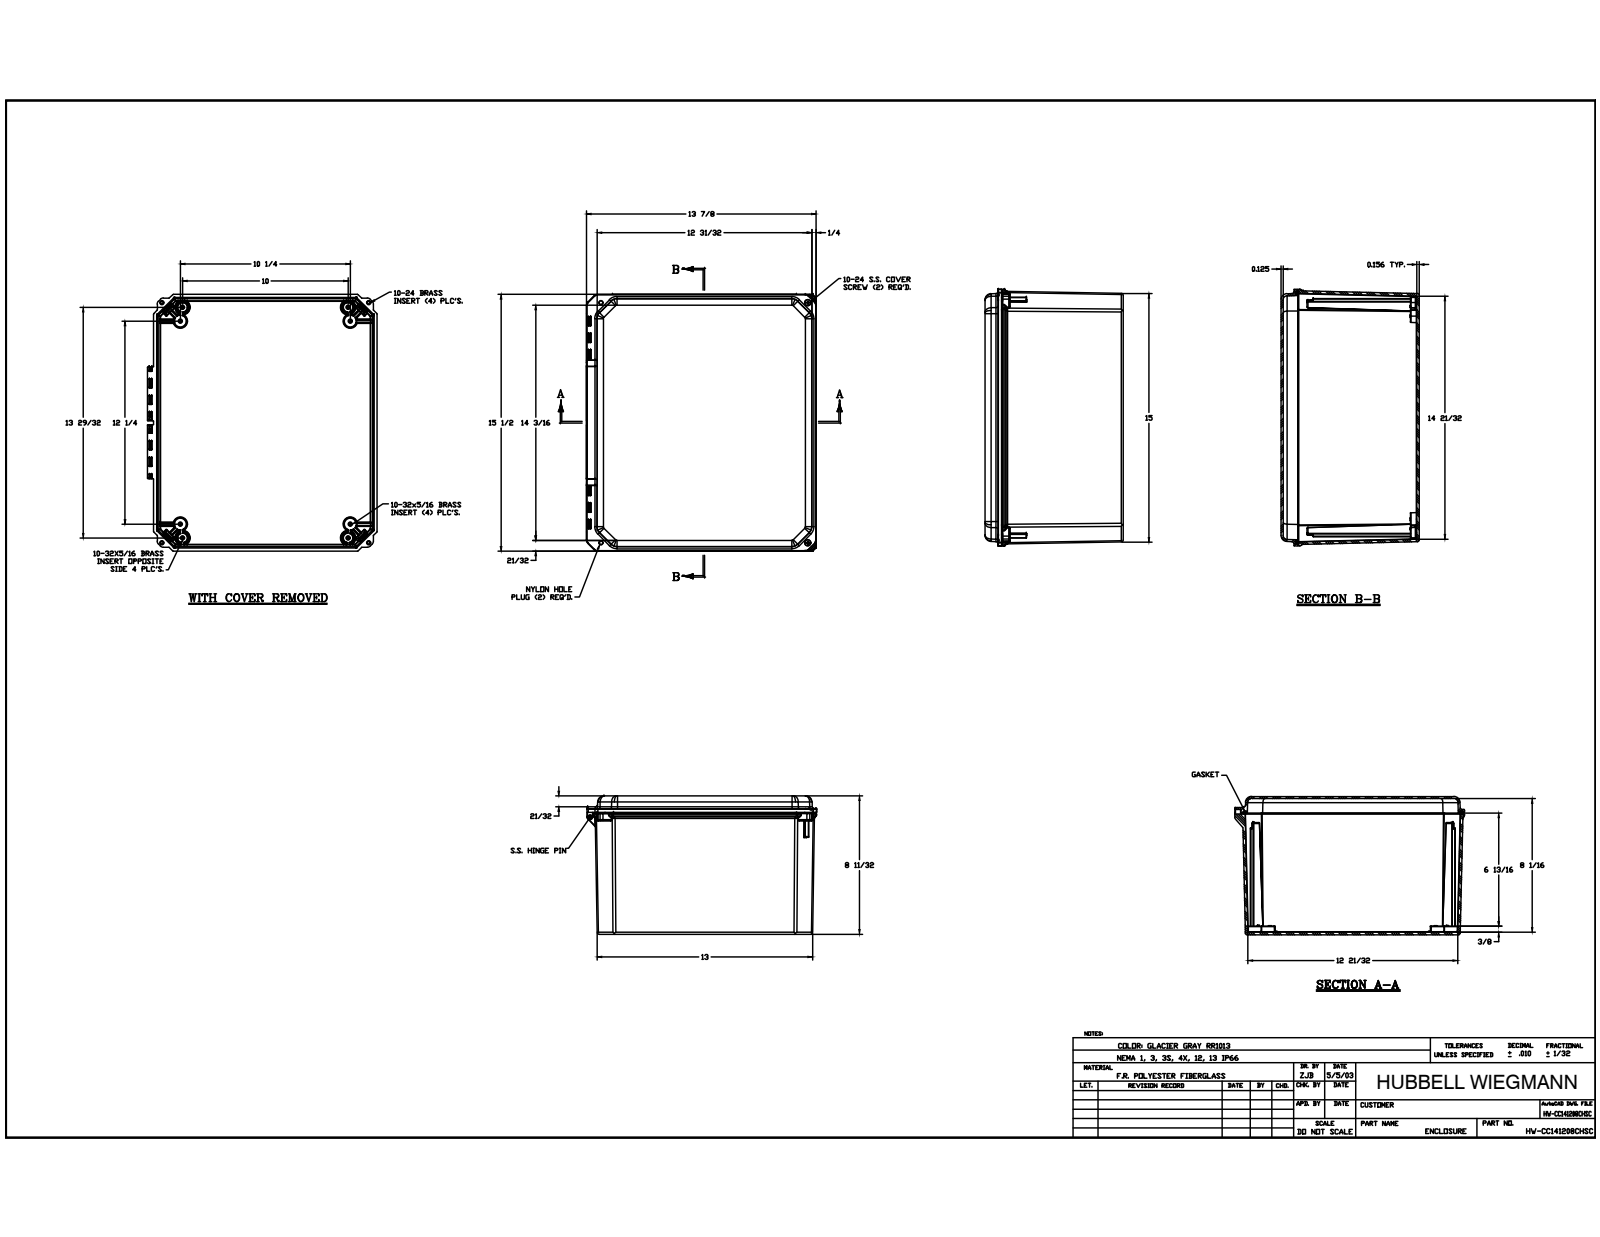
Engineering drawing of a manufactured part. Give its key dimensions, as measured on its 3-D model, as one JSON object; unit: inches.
{"part_name": "HW-CC141208CHSC; DS141208BOX; BRASS INSERT-(; BRASS INSERT-(_1 (+7 more)", "step_written_by": "Autodesk Inventor 2017 (CONFIG_CONTROL_DESIGN)", "units": "inches", "bodies": {"solids": 23, "faces": 2128, "planar": 603, "cylindrical": 800, "other": 725}, "overall_size": [15.494, 13.865, 8.343], "volume_in3": 134.6, "surface_area_in2": 1786, "round_holes": [[0.156, 12], [0.152, 8], [0.219, 4], [0.252, 4], [0.312, 4], [0.15, 2], [0.137, 1]], "round_bosses_or_shafts": [[0.246, 12], [0.45, 2], [0.209, 2], [0.199, 2], [0.135, 1]], "partial_cylinders_radius": [[0.01, 202], [0.005, 116], [0.02, 59], [0.03, 38], [0.125, 29], [0.03, 24], [0.09, 24], [0.25, 24]], "face_to_face_distances": [0.125, 0.156, 8.187, 8.343, 8.218, 8.062, 0.16, 0.159, 7.343, 1], "hole_center_spacings": [11.425, 0.828, 1.281, 1.584, 10.158, 11.249, 13.069, 13.417]}
